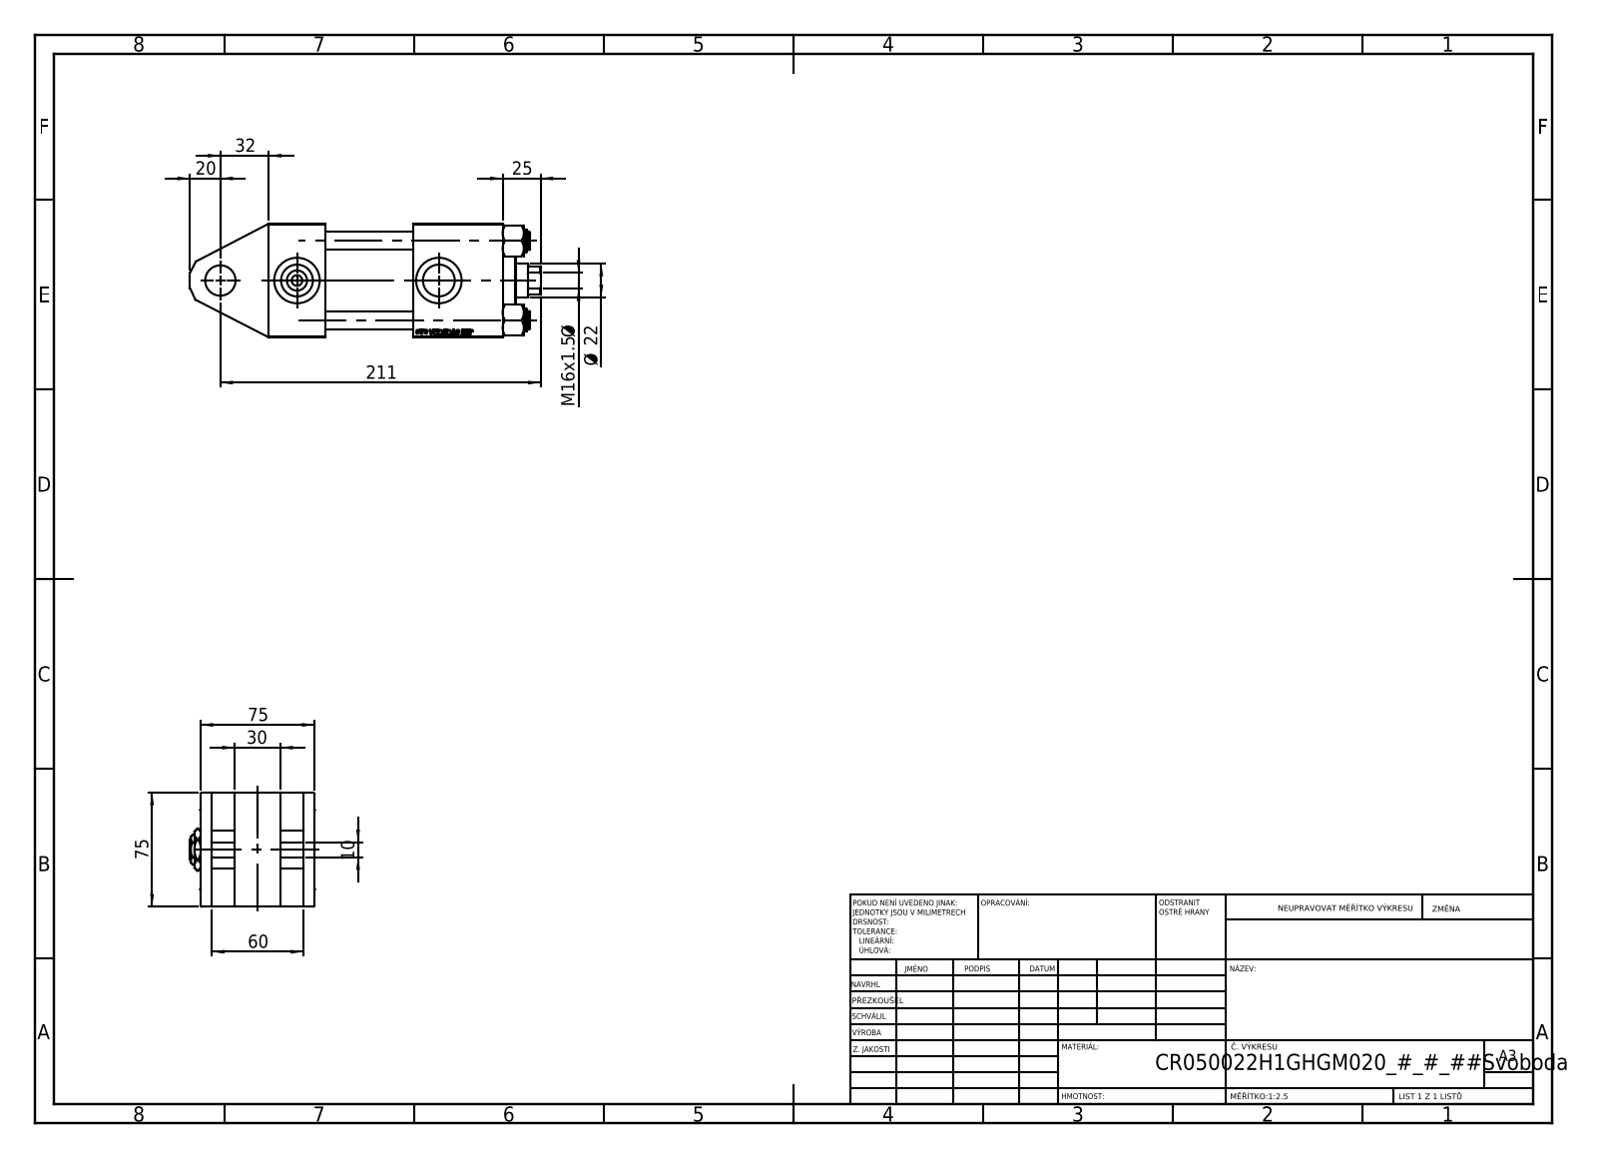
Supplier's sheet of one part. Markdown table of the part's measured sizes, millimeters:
| quantity | value |
| --- | --- |
| part name | NUT_M5_H; Zatka_pro_OIL_PORT; V215CR_H_Body; V215_VC_A (+2 more) |
| STEP written by | SolidWorks 2019 (CONFIG_CONTROL_DESIGN) |
| units | millimeters |
| bodies | 12 solids, 1176 faces (541 planar, 87 cylindrical, 548 other) |
| overall size | 231 × 82.27 × 75 |
| volume | 730 736 mm³ |
| surface area | 164 839 mm² |
| round holes (diameter × count) | 12 × 4, 7 × 2, 20.96 × 2, 30 × 2, 10.5 × 1, 20 × 1, 22 × 1, 25 × 1, 41 × 1, 50 × 1, 53 × 1 |
| round bosses / shafts (diameter × count) | 15 × 4, 56 × 1, 34 × 1 |
| partial cylindrical surfaces (radius × count) | 10.5 × 1 |
| main face-to-face distances | 75, 117, 67.5, 7.5, 45, 22.5, 52.5, 15, 95, 37 |
| hole center spacings | 36.98, 52.3, 73.96, 50.5, 93.5, 144 |
